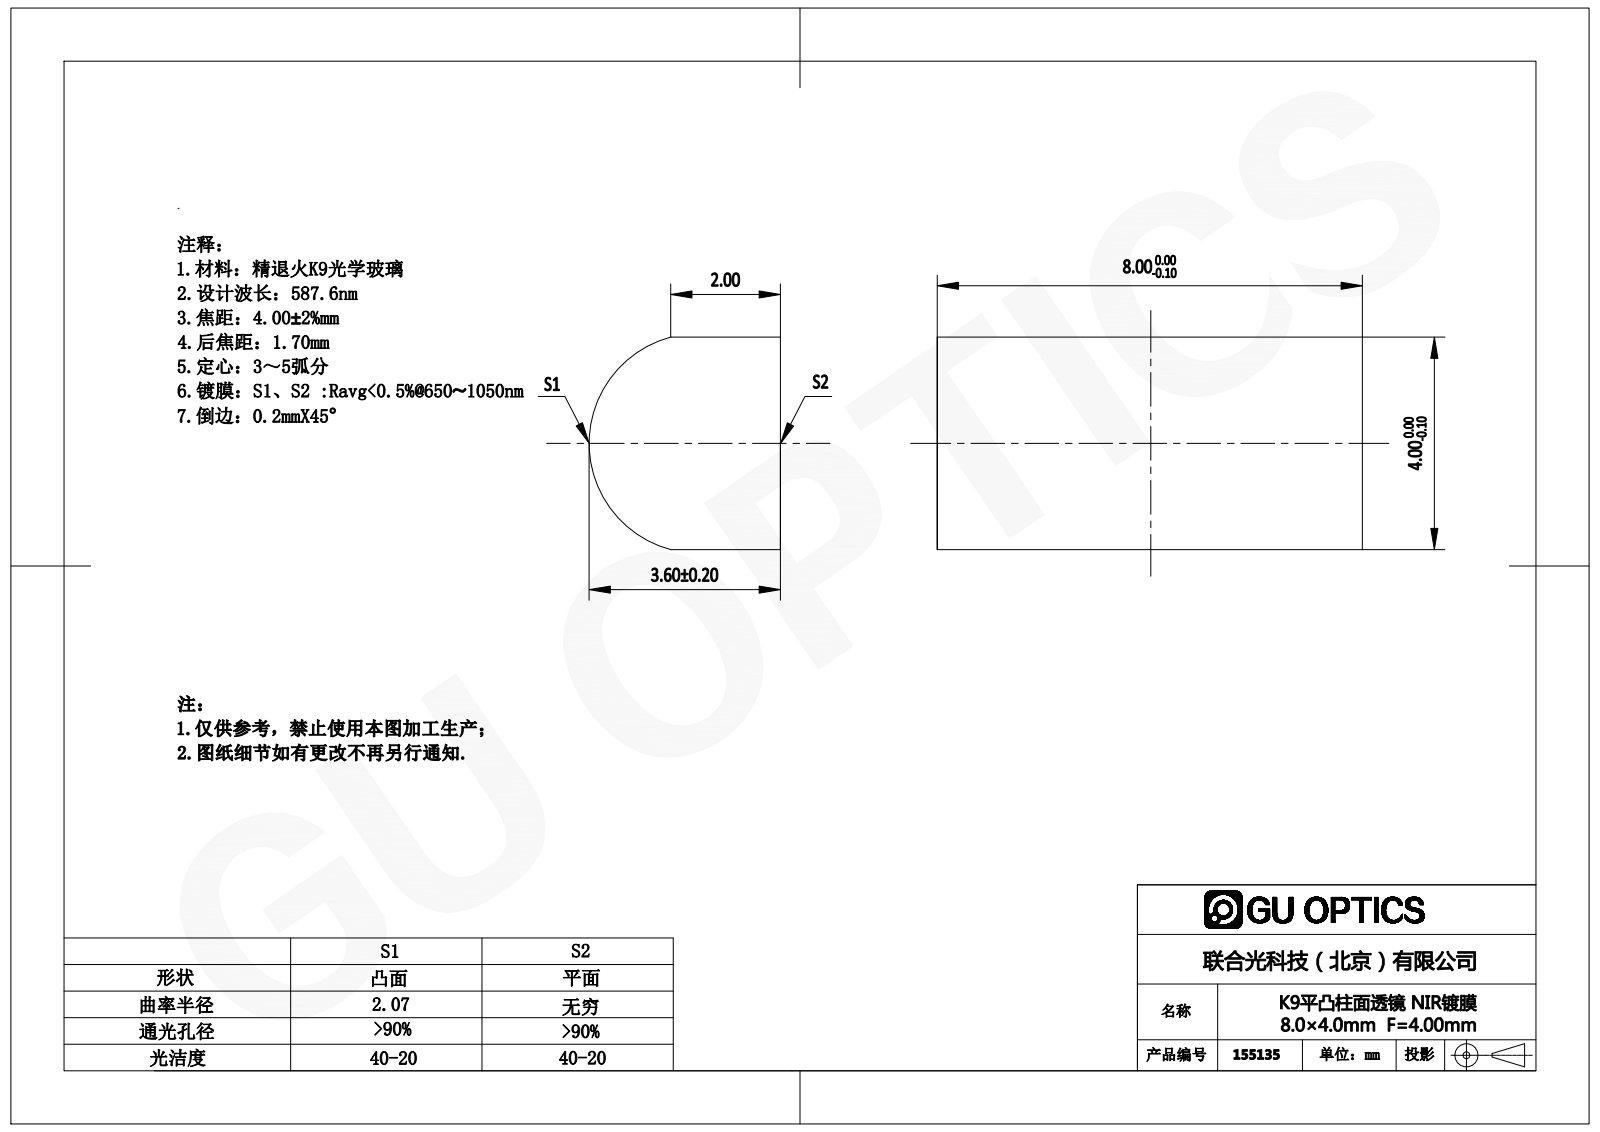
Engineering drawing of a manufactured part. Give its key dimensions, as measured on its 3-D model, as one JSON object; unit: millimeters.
{"part_name": "155003", "step_written_by": "SolidWorks 2016 (AUTOMOTIVE_DESIGN)", "units": "millimeters", "bodies": {"solids": 1, "faces": 6, "planar": 5, "cylindrical": 1, "other": 0}, "overall_size": [8, 4, 3.6], "volume_mm3": 102, "surface_area_mm2": 134, "partial_cylinders_radius": [[2.07, 1]], "face_to_face_distances": [4, 8]}
